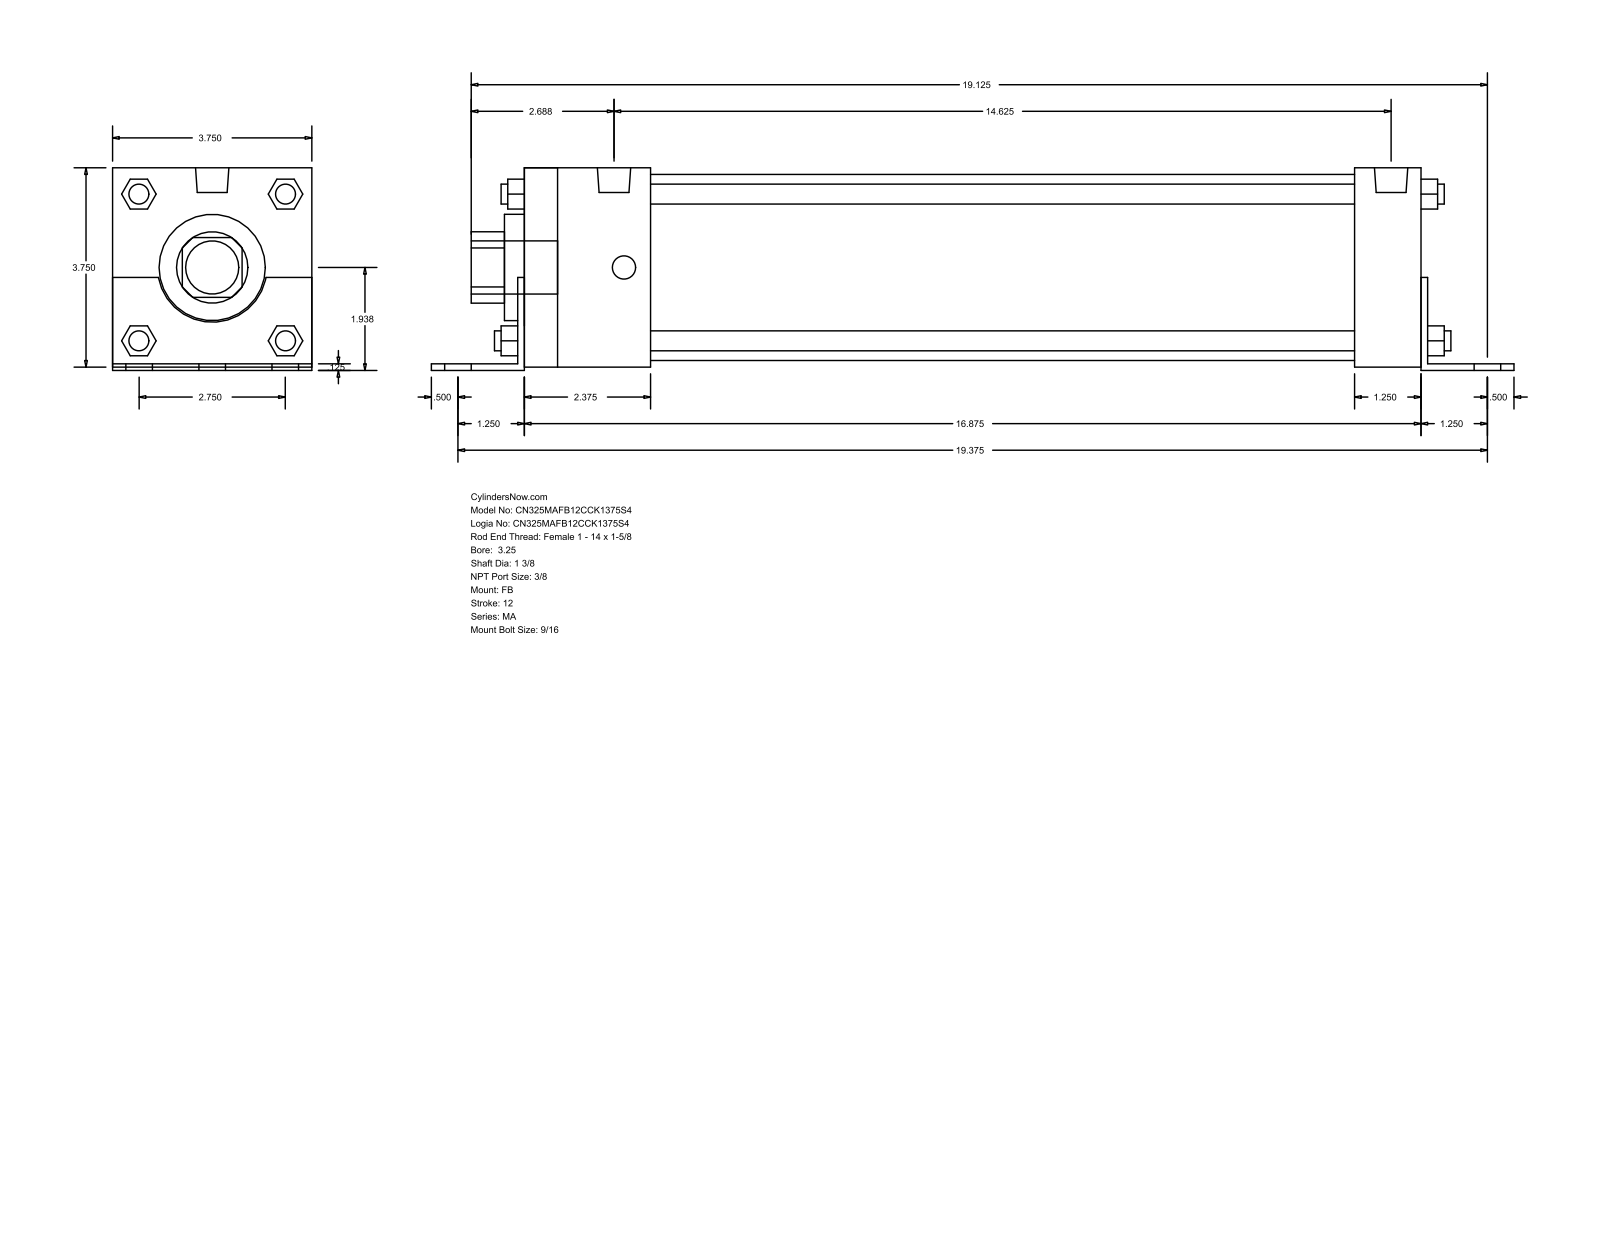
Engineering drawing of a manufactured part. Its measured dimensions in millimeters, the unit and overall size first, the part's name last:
Units: millimetres
Overall size (bounding box): 517.52 × 96.84 × 95.25
Round holes (diameter × count): ⌀34.92 ×1, ⌀50.8 ×1, ⌀88.9 ×1
Round bosses / shafts (diameter × count): ⌀14.29 ×6, ⌀11.11 ×4, ⌀9.53 ×4, ⌀15.93 ×2, ⌀25.4 ×1
Partial cylindrical surfaces — rounded edges, fillets, slot ends (radius × count): R17.06 ×1, R26.16 ×1
Main face-to-face distances: 95.24, 3.17, 1.59, 96.83, 1.58, 93.66, 3.18, 428.62, 431.8, 31.75
Bodies: 0 solids, 140 faces (105 planar, 35 cylindrical, 0 other)
Part name (STEP PRODUCT): MA_FB__0325_1.375
STEP written by: GSSL Pune (CONFIG_CONTROL_DESIGN)
